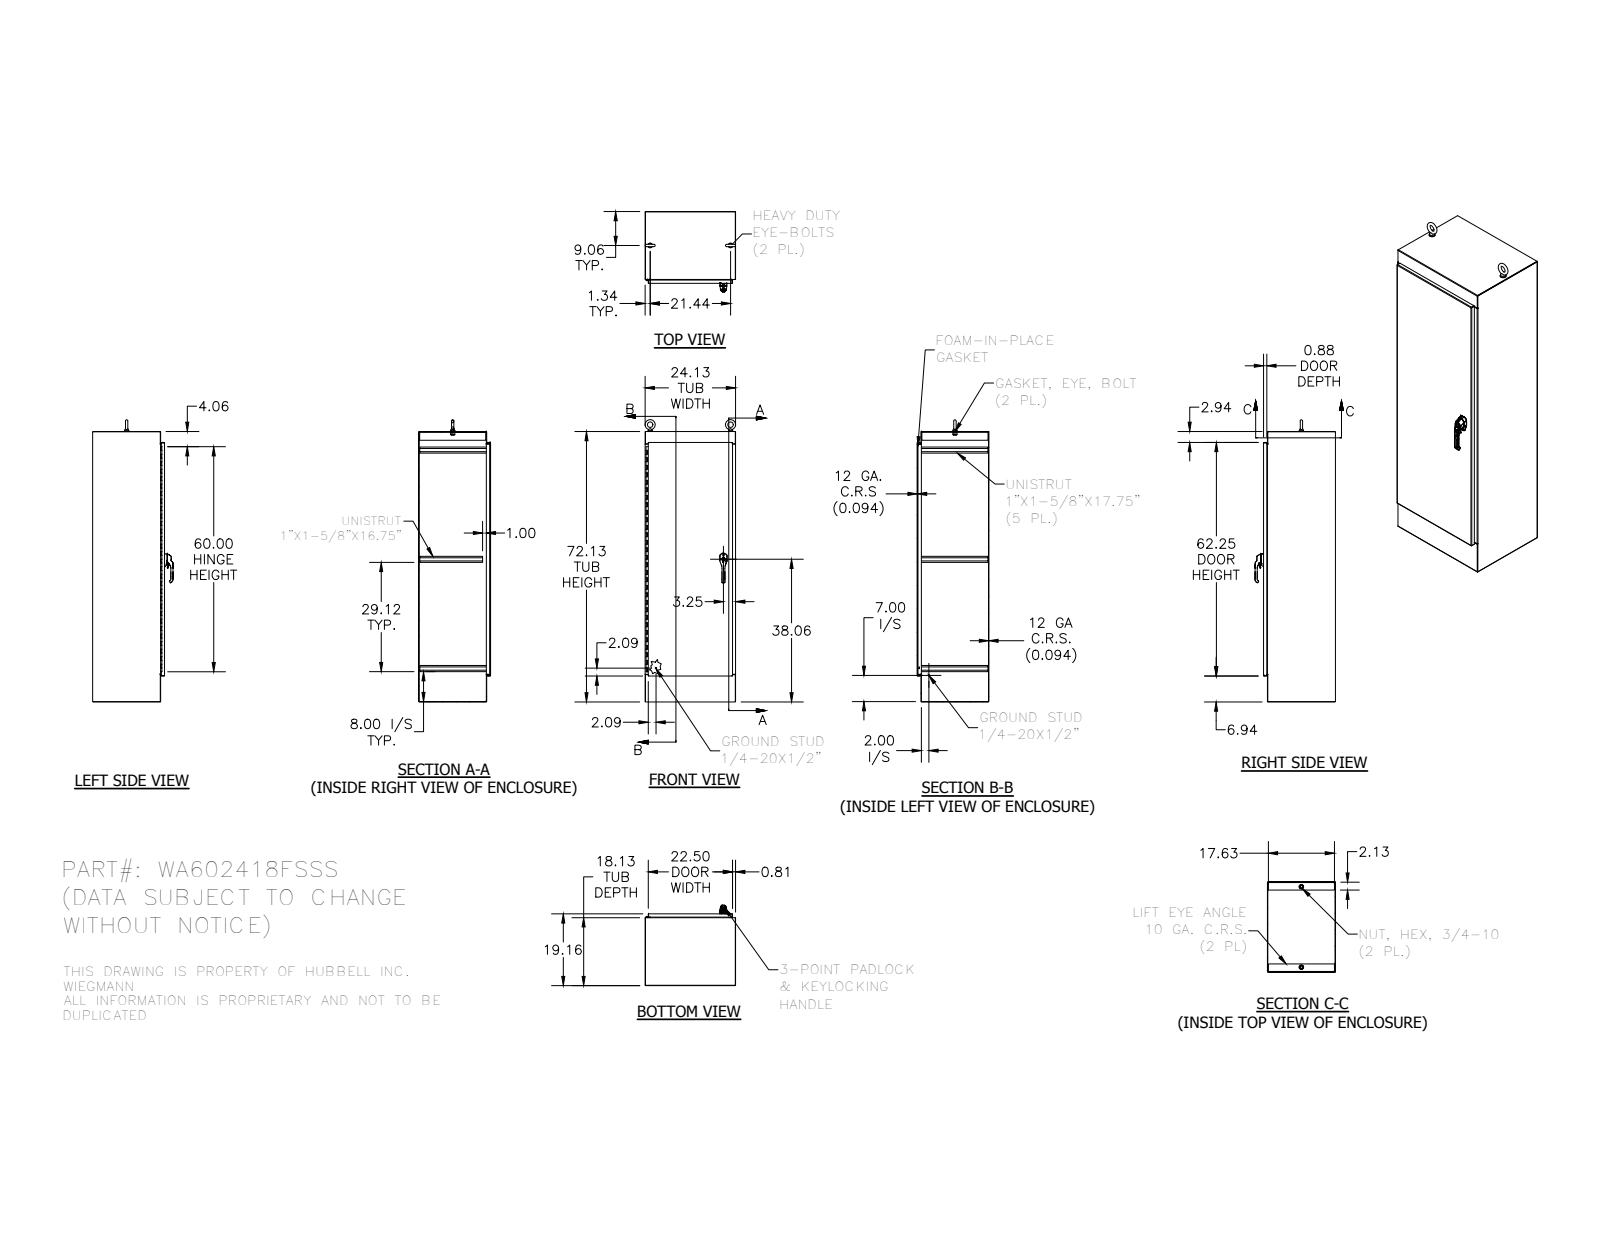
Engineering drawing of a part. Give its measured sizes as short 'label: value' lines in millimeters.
name: WA722418FSBLR; WA2418FSTOP; WA2418FSBTM; WA7224FSDR (+8 more)
written by: Autodesk Inventor 2014 (AUTOMOTIVE_DESIGN)
unit: mm
bodies: 46 solids, 2879 faces (1224 planar, 1007 cylindrical, 648 other)
size: 1911.29 × 612.77 × 543.79
volume: 12 680 000 mm³; area: 10 560 000 mm²
holes: 8× ⌀7.02, 4× ⌀5.08, 3× ⌀5.4, 3× ⌀7.11, 2× ⌀8, 2× ⌀10.2, 2× ⌀10.33, 2× ⌀10.5, 2× ⌀16.31, 2× ⌀20.64, 1× ⌀3.1, 1× ⌀3.15
bosses: 3× ⌀6.35, 2× ⌀31.75, 2× ⌀28.45, 2× ⌀19.05, 2× ⌀13.5, 2× ⌀13.37, 2× ⌀11.05, 2× ⌀8.56
rounds: 178× R0.5, 101× R0.3, 23× R0.47, 16× R0.25, 16× R0.79, 14× R1.35, 14× R2, 14× R3.17
face distances: 2.38, 484.3, 610.4, 608.02, 481.92, 486.68, 612.78, 1829.6, 458, 26.3
hole spacings: 9.66, 9.7, 9.71, 19.36, 19.4, 22.5, 29.06, 32.29
